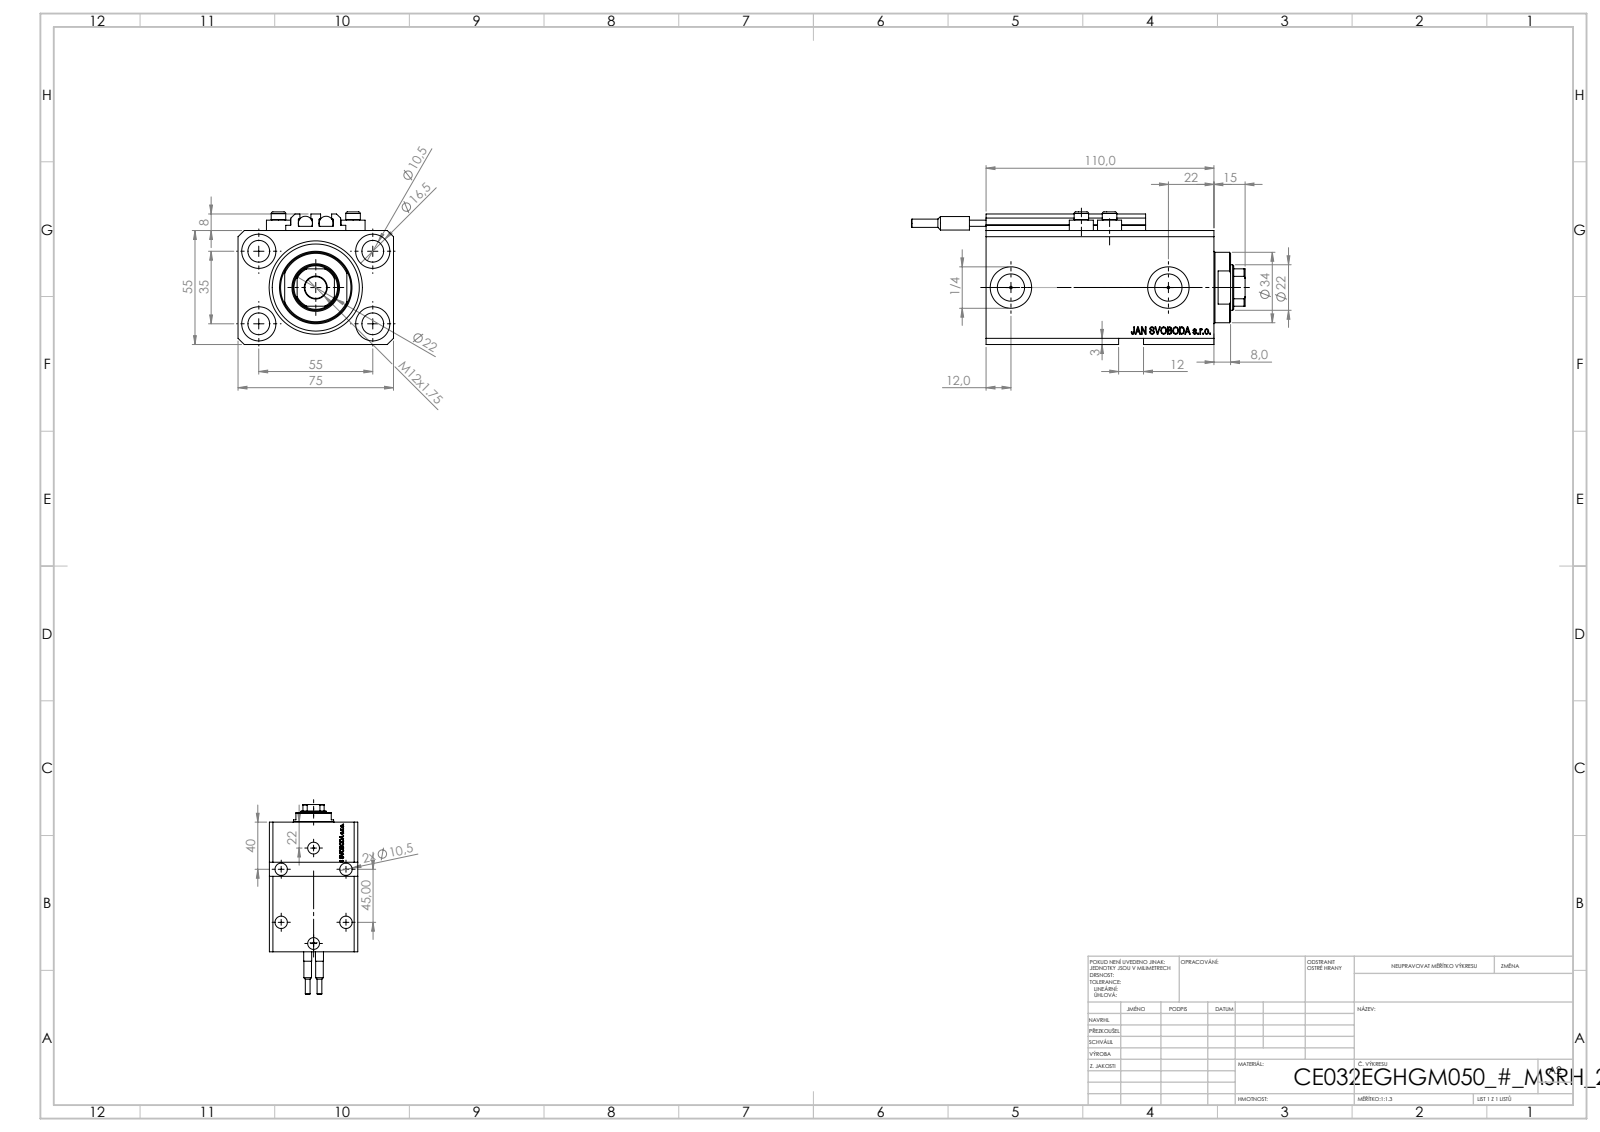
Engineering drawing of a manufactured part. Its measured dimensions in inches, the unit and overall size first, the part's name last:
Units: inches
Overall size (bounding box): 6.339 × 2.953 × 2.52
Round holes (diameter × count): ⌀0.413 ×9, ⌀0.049 ×4, ⌀0.157 ×4, ⌀0.65 ×4, ⌀0.394 ×2, ⌀0.518 ×2, ⌀0.787 ×2, ⌀0.866 ×1, ⌀1.26 ×1, ⌀1.772 ×1
Round bosses / shafts (diameter × count): ⌀0.457 ×4, ⌀0.276 ×4, ⌀0.268 ×2, ⌀0.256 ×2, ⌀0.157 ×2, ⌀1.339 ×1
Partial cylindrical surfaces — rounded edges, fillets, slot ends (radius × count): R0.008 ×10, R0.413 ×1
Main face-to-face distances: 2.165, 2.953, 0.118, 0.591, 4.331, 2.244, 3.74, 0.39, 3.35, 3.941
Hole centre spacings: 1.283, 1.294, 2.165, 2.706, 0.535, 0.555, 0.907, 1.016
Volume: 23.49 in³ · Surface area: 152.5 in²
Bodies: 10 solids, 1136 faces (546 planar, 158 cylindrical, 432 other)
Part name (STEP PRODUCT): V250CE_C_VCP; ALLEN BOLT V250CE; V250CE_VC_E; SWITCH_V250CE (+1 more)
STEP written by: SolidWorks 2019 (CONFIG_CONTROL_DESIGN)
